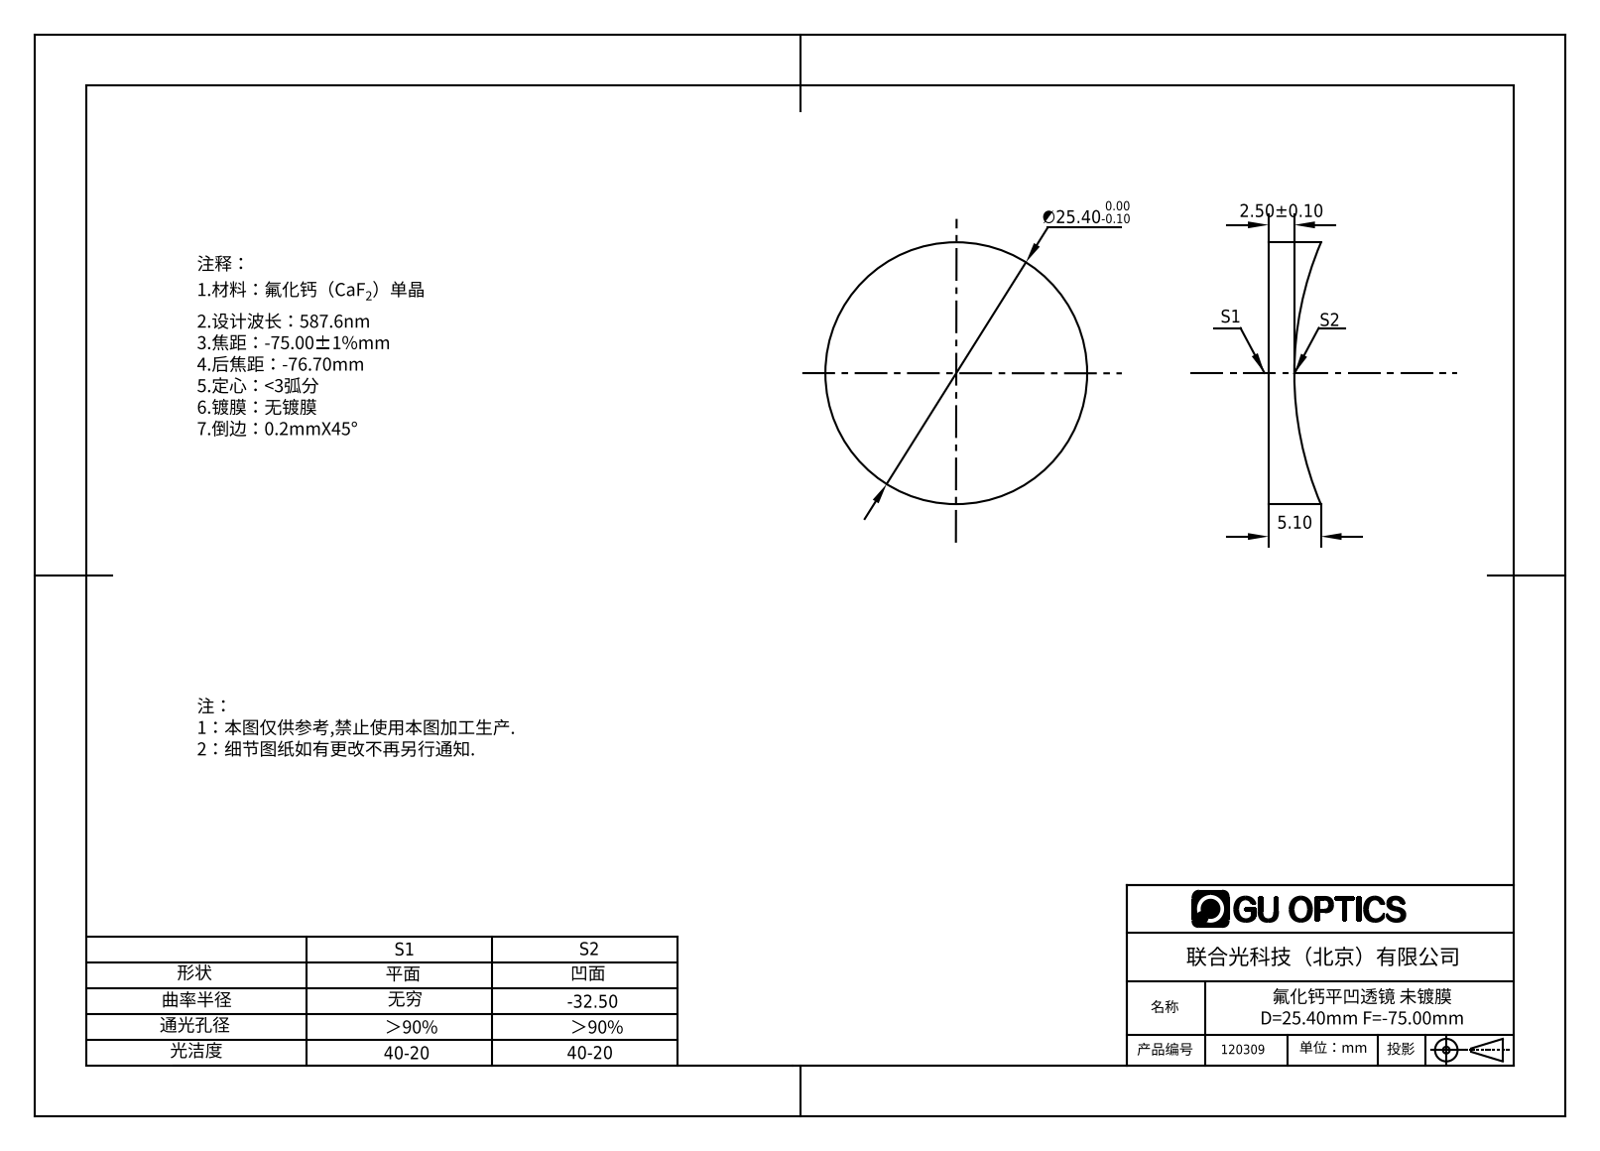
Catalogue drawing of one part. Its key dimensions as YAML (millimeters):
part_name: "120309"
step_written_by: "SolidWorks 2016 (AUTOMOTIVE_DESIGN)"
units: millimeters
bodies: {solids: 1, faces: 5, planar: 1, cylindrical: 2, other: 2}
overall_size: [25.4, 25.4, 5.08]
volume: 1912
surface_area: 1440
round_bosses_or_shafts:
  - {diameter: 25.4, count: 1}
